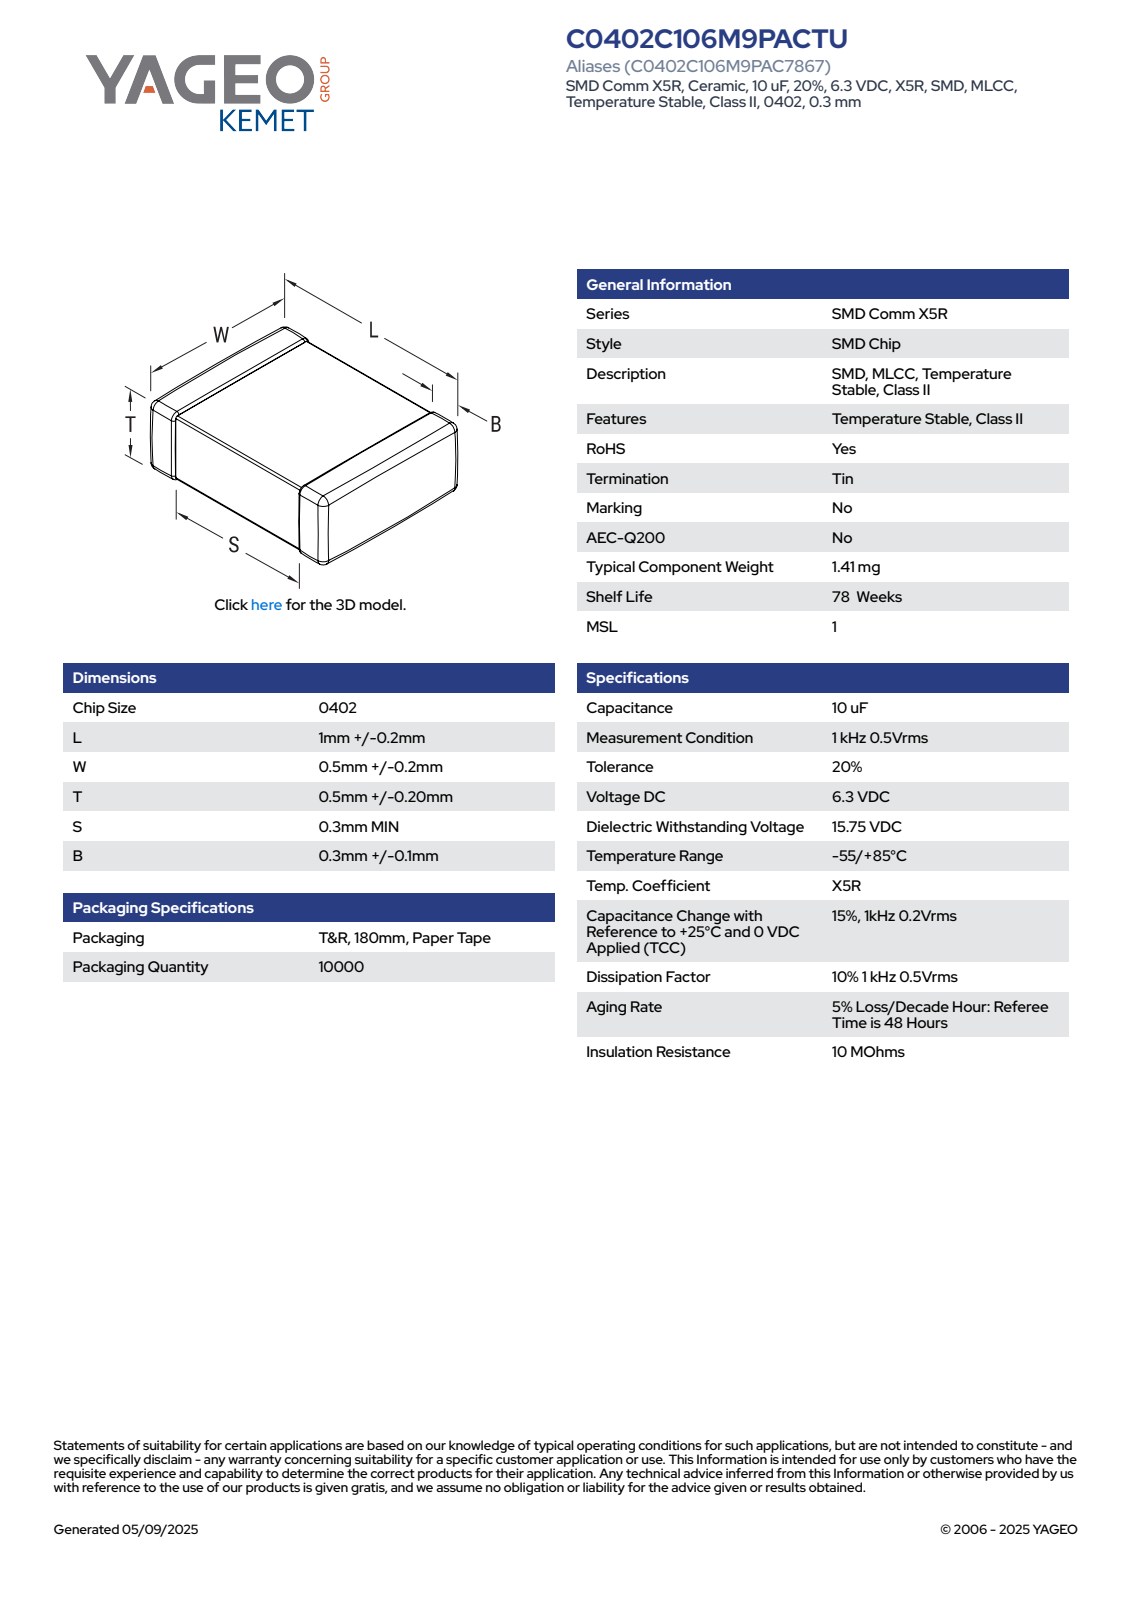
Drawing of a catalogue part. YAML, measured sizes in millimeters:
part_name: "CCS_CCSTD_0402_L1.2W0.7T0.7B0.3"
step_written_by: "SolidWorks 2021 (AUTOMOTIVE_DESIGN)"
units: millimeters
bodies: {solids: 4, faces: 125, planar: 71, cylindrical: 38, other: 16}
overall_size: [1.2, 0.7, 0.7]
volume: 0.563
surface_area: 4
face_to_face_distances: [0.69, 0.68, 0.7, 1.2, 0.55, 0.65, 0.6, 0.42, 0.45, 0.31]
